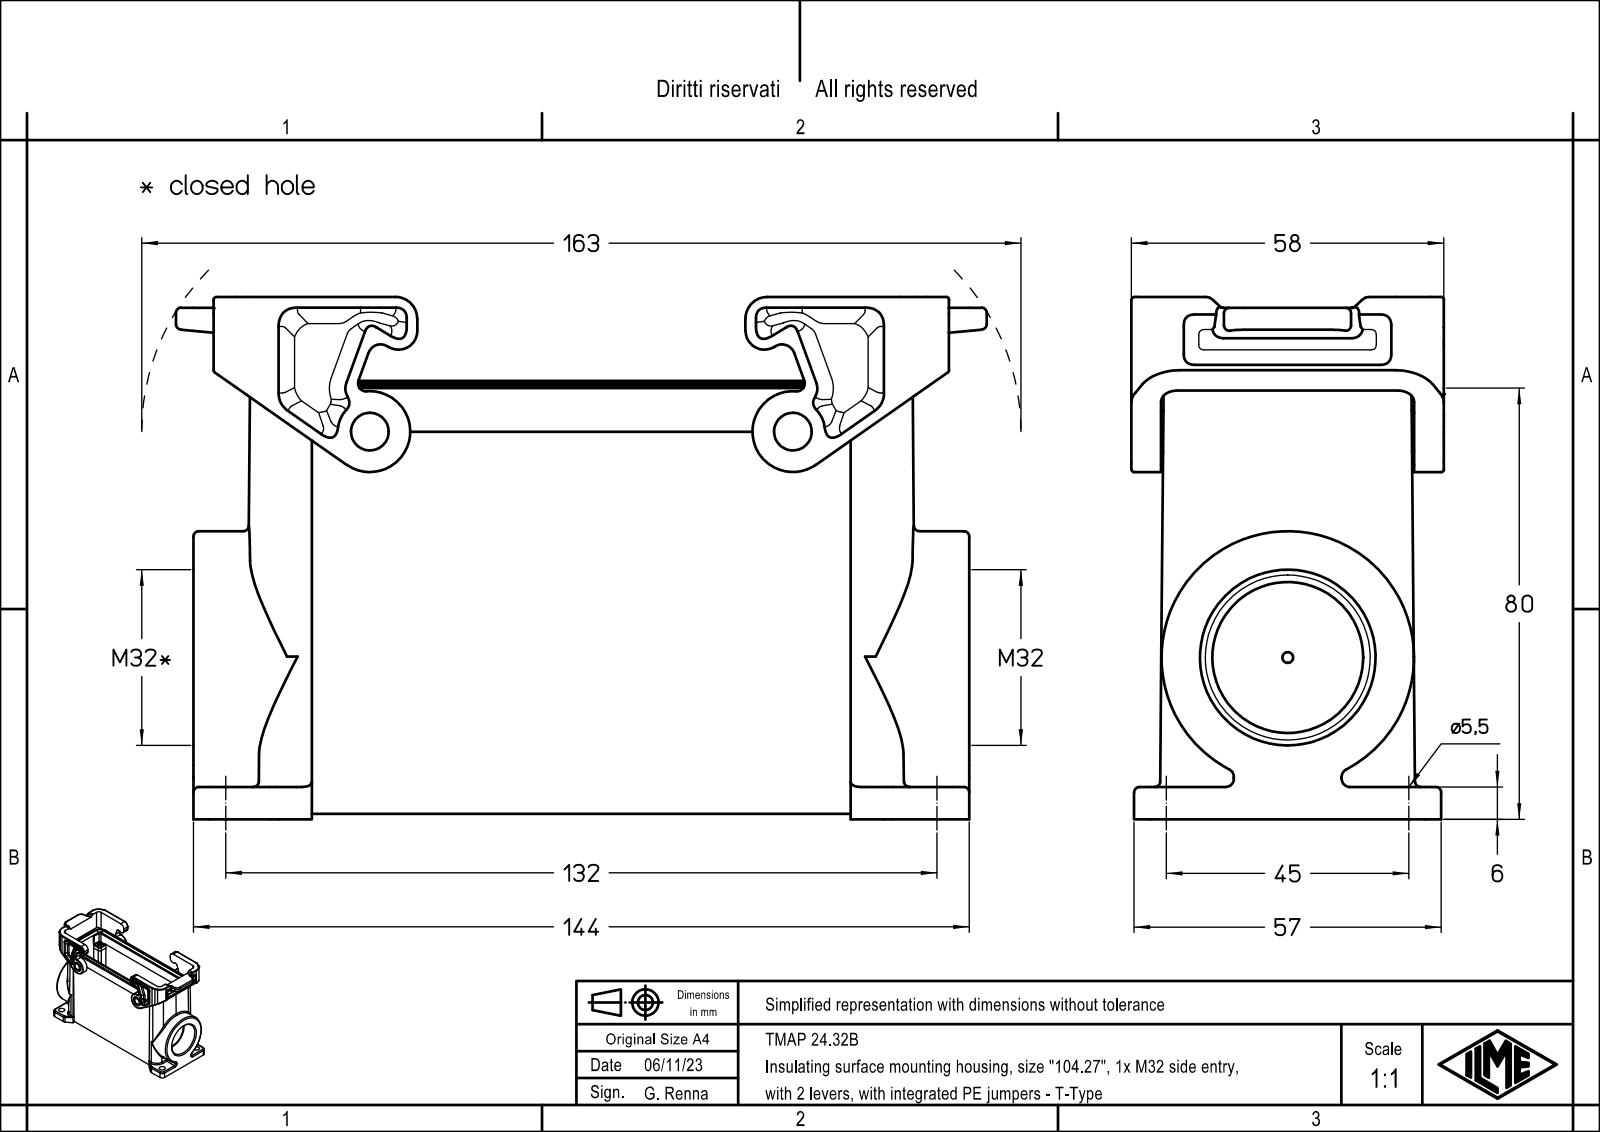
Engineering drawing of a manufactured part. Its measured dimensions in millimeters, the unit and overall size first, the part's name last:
Units: millimetres
Overall size (bounding box): 150.5 × 96.9 × 58
Round holes (diameter × count): ⌀3.5 ×4, ⌀5.5 ×4, ⌀28 ×1, ⌀30.6 ×1
Round bosses / shafts (diameter × count): ⌀7 ×2, ⌀46.87 ×1
Partial cylindrical surfaces — rounded edges, fillets, slot ends (radius × count): R2 ×20, R3 ×20, R1.5 ×18, R1 ×16, R1.3 ×12, R6 ×8, R7 ×8, R4 ×6
Main face-to-face distances: 35.2, 5.5, 5.9, 41.1, 1, 6.5, 6.3, 6.6, 40.4, 40.7
Hole centre spacings: 16.64, 38.63, 118.34, 123.37, 27, 45, 104, 107.45
Volume: 229 418 mm³ · Surface area: 85 334 mm²
Bodies: 1 solid, 606 faces (360 planar, 194 cylindrical, 52 other)
Part name (STEP PRODUCT): TMAP 24.32B
STEP written by: Creo Elements/Direct Modeling 20.1B 02-Apr-2019 (C) Parametric Technology GmbH (AUTOMOTIVE_DESIGN)
